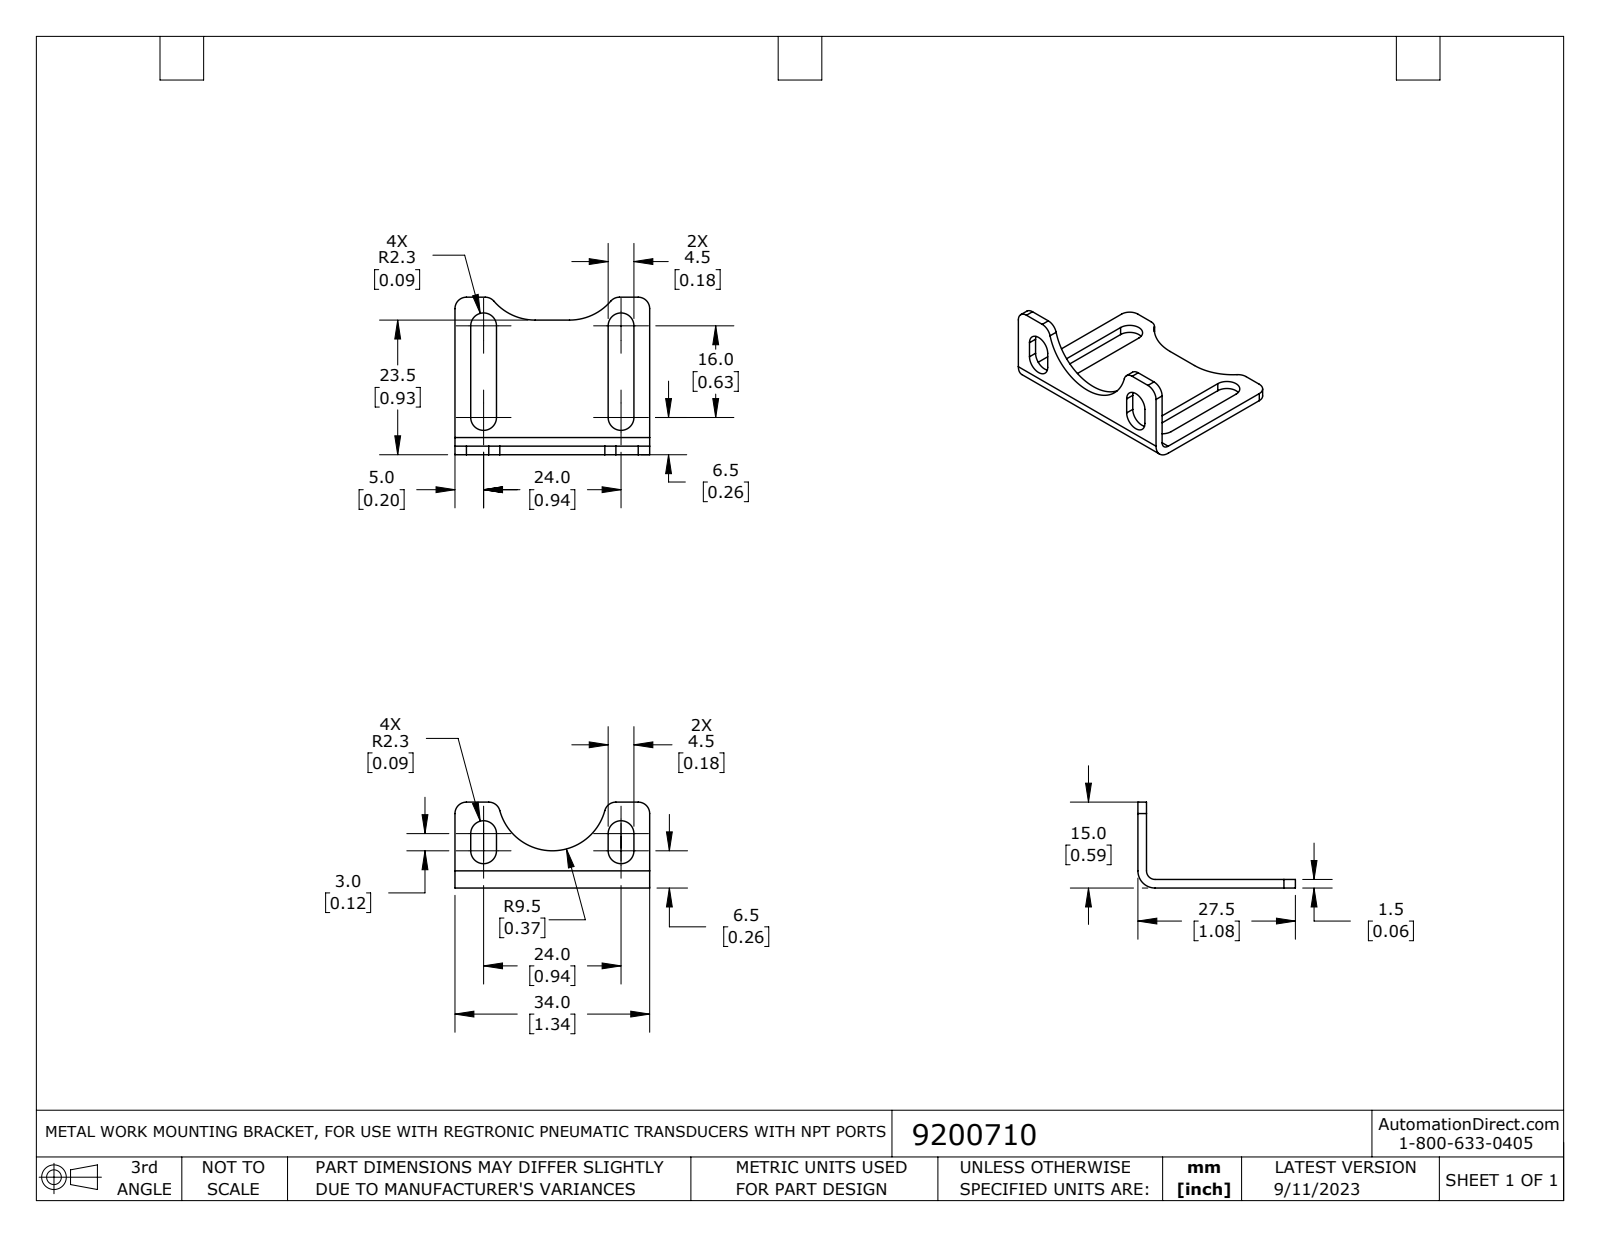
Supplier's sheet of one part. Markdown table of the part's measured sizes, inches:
| quantity | value |
| --- | --- |
| part name | 9200710 |
| STEP written by | SolidWorks 2021 (AUTOMOTIVE_DESIGN) |
| units | inches |
| bodies | 1 solid, 40 faces (19 planar, 21 cylindrical, 0 other) |
| overall size | 1.339 × 1.083 × 0.591 |
| volume | 0.085 in³ |
| surface area | 3.556 in² |
| partial cylindrical surfaces (radius × count) | 0.079 × 8, 0.089 × 8, 0.374 × 3, 0.059 × 1, 0.118 × 1 |
| main face-to-face distances | 0.059, 0.108, 0.285, 1.053, 1.23, 0.945, 0.177, 1.339, 1.122, 0.768 |
